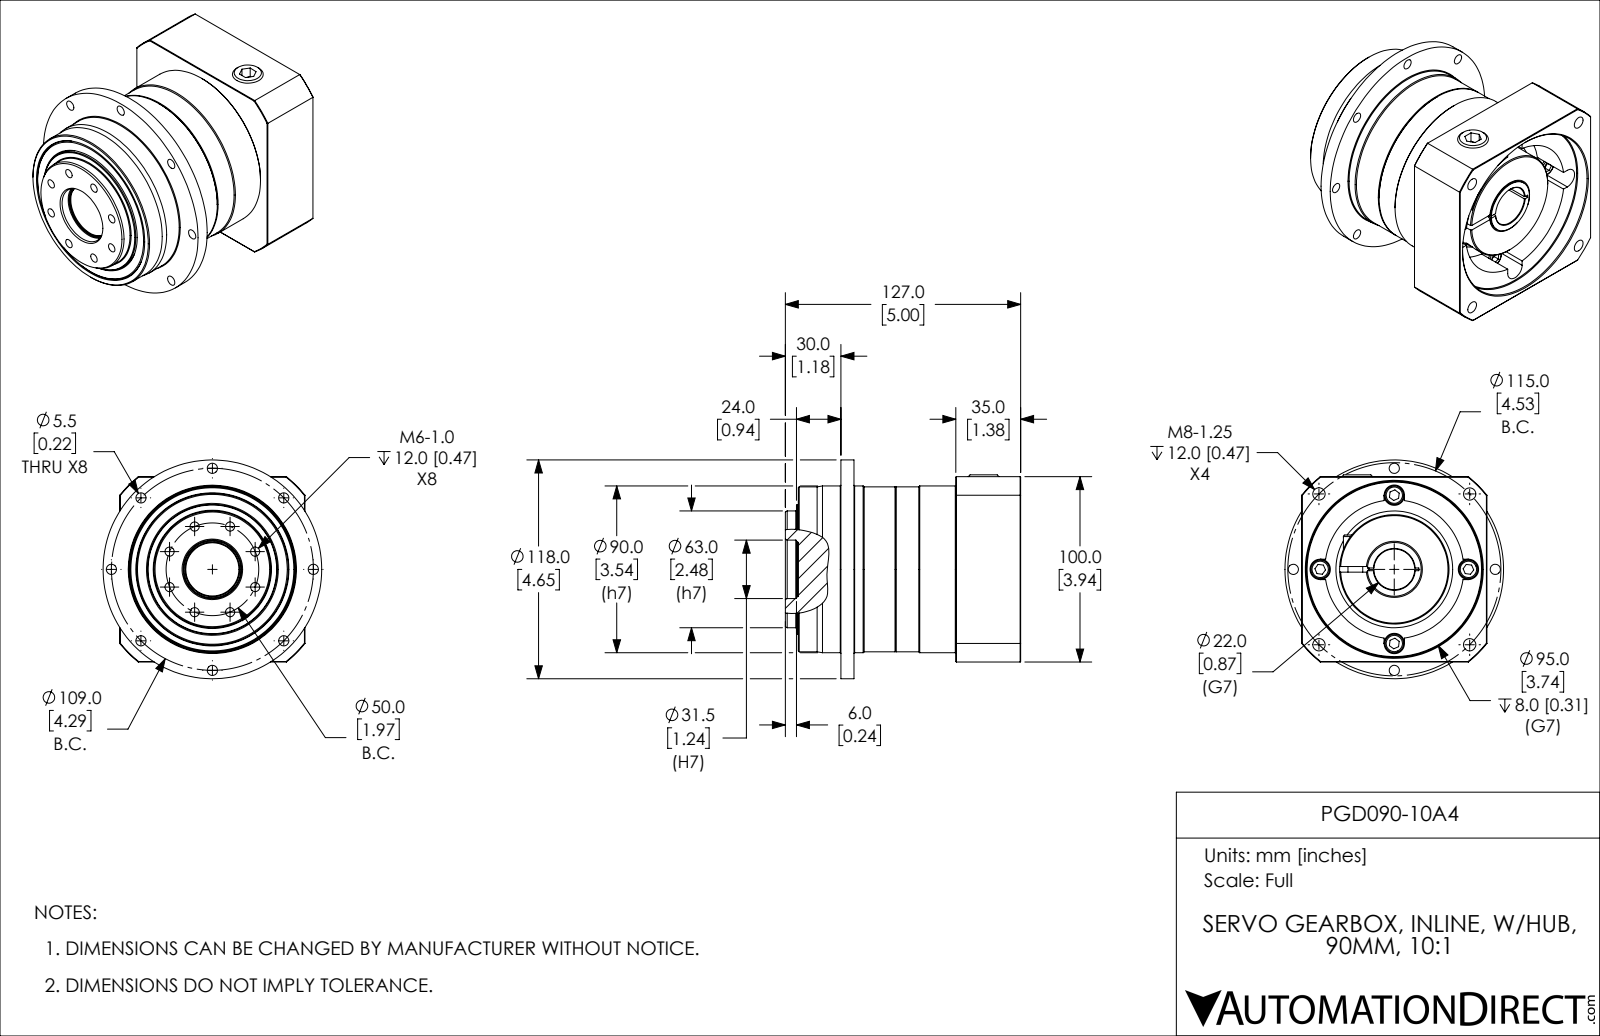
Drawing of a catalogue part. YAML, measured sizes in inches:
part_name: "PGD090-10A4"
step_written_by: "SolidWorks 2015 (AUTOMOTIVE_DESIGN)"
units: inches
bodies: {solids: 7, faces: 338, planar: 127, cylindrical: 146, other: 65}
overall_size: [5, 4.646, 4.646]
volume: 47.55
surface_area: 173.6
round_holes:
  - {diameter: 0.217, count: 8}
  - {diameter: 0.194, count: 7}
  - {diameter: 0.262, count: 4}
  - {diameter: 0.315, count: 3}
  - {diameter: 0.194, count: 1}
  - {diameter: 0.197, count: 1}
  - {diameter: 0.512, count: 1}
  - {diameter: 0.567, count: 1}
  - {diameter: 0.709, count: 1}
  - {diameter: 0.787, count: 1}
  - {diameter: 0.866, count: 1}
  - {diameter: 1.041, count: 1}
round_bosses_or_shafts:
  - {diameter: 0.394, count: 4}
  - {diameter: 4.646, count: 1}
  - {diameter: 3.543, count: 1}
  - {diameter: 3.504, count: 1}
  - {diameter: 2.48, count: 1}
  - {diameter: 1.654, count: 1}
  - {diameter: 1.142, count: 1}
  - {diameter: 0.654, count: 1}
partial_cylinders:
  - {radius: 0.217, count: 4}
  - {radius: 0.276, count: 1}
  - {radius: 2.52, count: 1}
face_to_face_distances: [3.35, 0.157, 0.909, 3.937, 3.346, 2.441, 2.283, 1.067, 4.256, 1.063]
hole_center_spacings: [1.293, 2.681, 3.078, 0.984, 1.392, 1.406, 1.819, 1.989]
